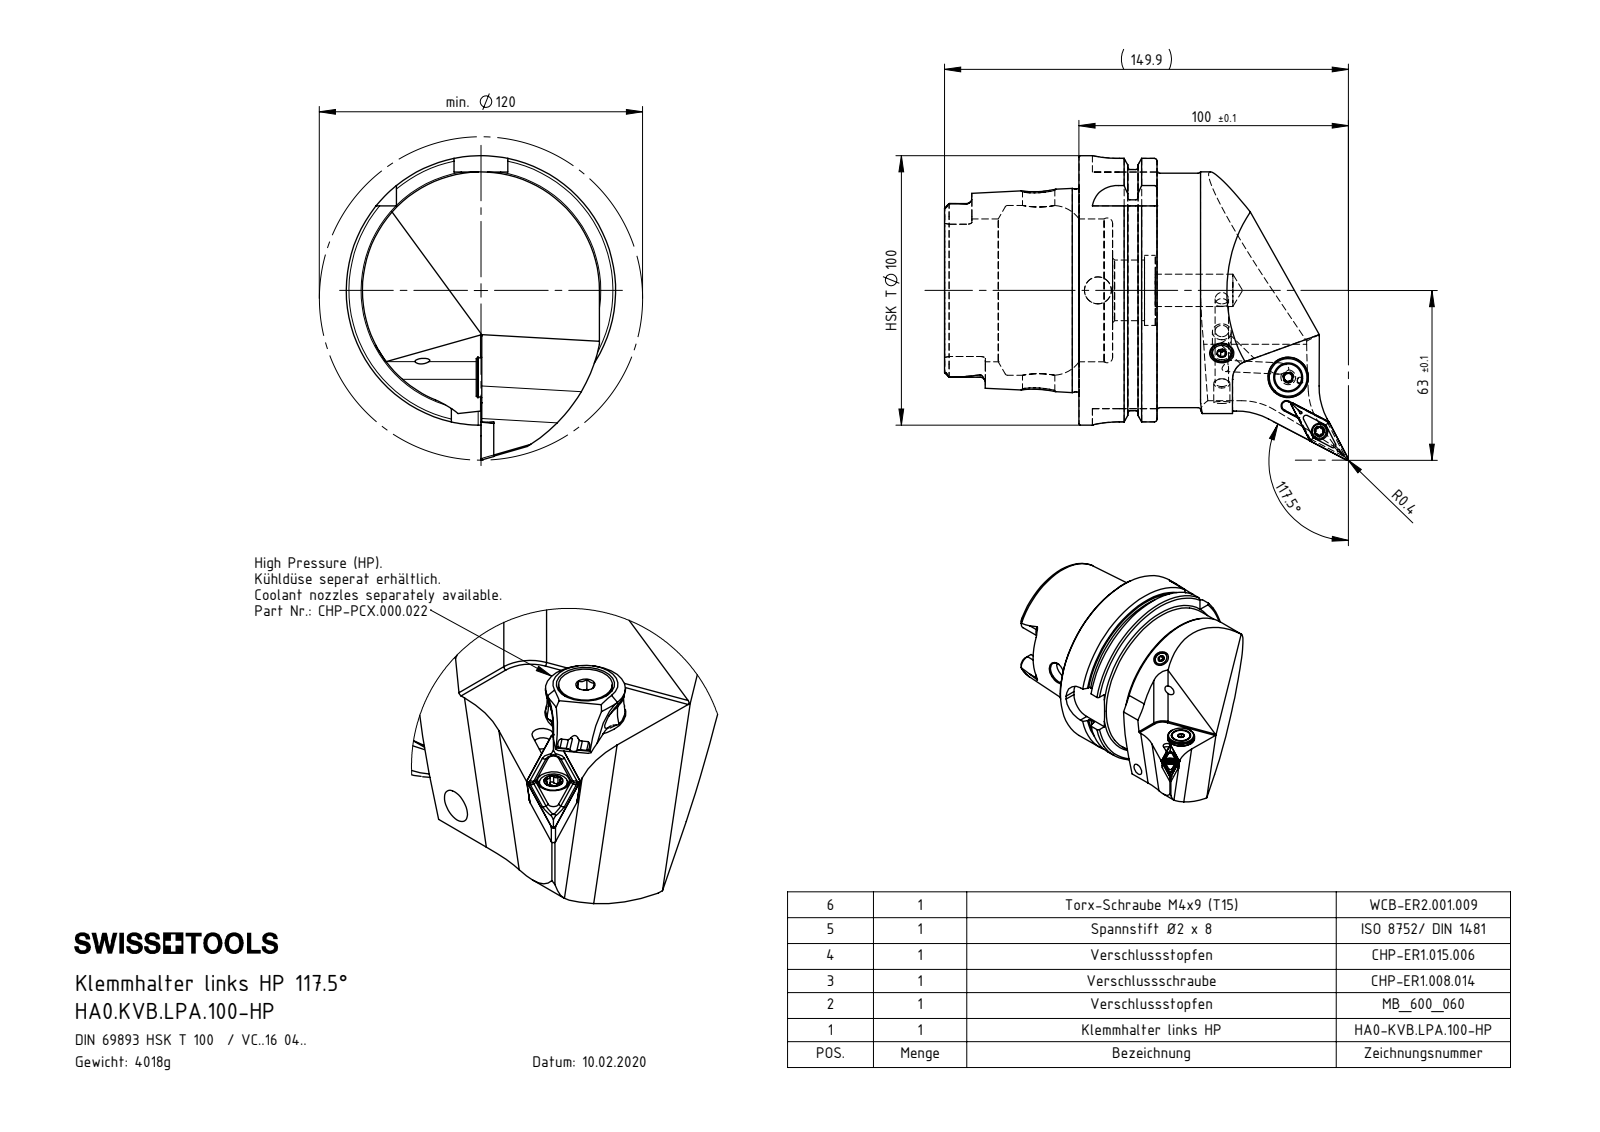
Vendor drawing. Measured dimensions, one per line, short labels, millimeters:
name: HA0-KVB.LPA.100-HP_A_Fertigbearbeitung; CHP-ER1.015.006; HA0.KVB.LPA.100-HP; DIN 7991 - M5x15 (+7 more)
written by: SolidWorks 2017 (AUTOMOTIVE_DESIGN)
unit: mm
bodies: 10 solids, 332 faces (119 planar, 83 cylindrical, 130 other)
size: 149.89 × 112.99 × 100
volume: 511 129 mm³; area: 69 588 mm²
holes: 4× ⌀5, 2× ⌀4.2, 2× ⌀12, 1× ⌀1.2, 1× ⌀2, 1× ⌀2.5, 1× ⌀3, 1× ⌀3.3, 1× ⌀4.4, 1× ⌀5.2, 1× ⌀6, 1× ⌀6.1
bosses: 1× ⌀100, 1× ⌀91.95, 1× ⌀87, 1× ⌀75.26, 1× ⌀15, 1× ⌀13.4, 1× ⌀10, 1× ⌀8
rounds: 6× R0.34, 6× R0.59, 6× R1.9, 4× R10, 2× R0.5, 2× R4.83, 2× R4.88, 2× R26
face distances: 12.45, 28.95, 16.5, 49.9, 62.35, 78.85, 43.7, 87.8, 78.2, 28.3
hole spacings: 4.5, 2.25, 18.81, 18.91, 20.14, 20.24, 23.11, 23.22
